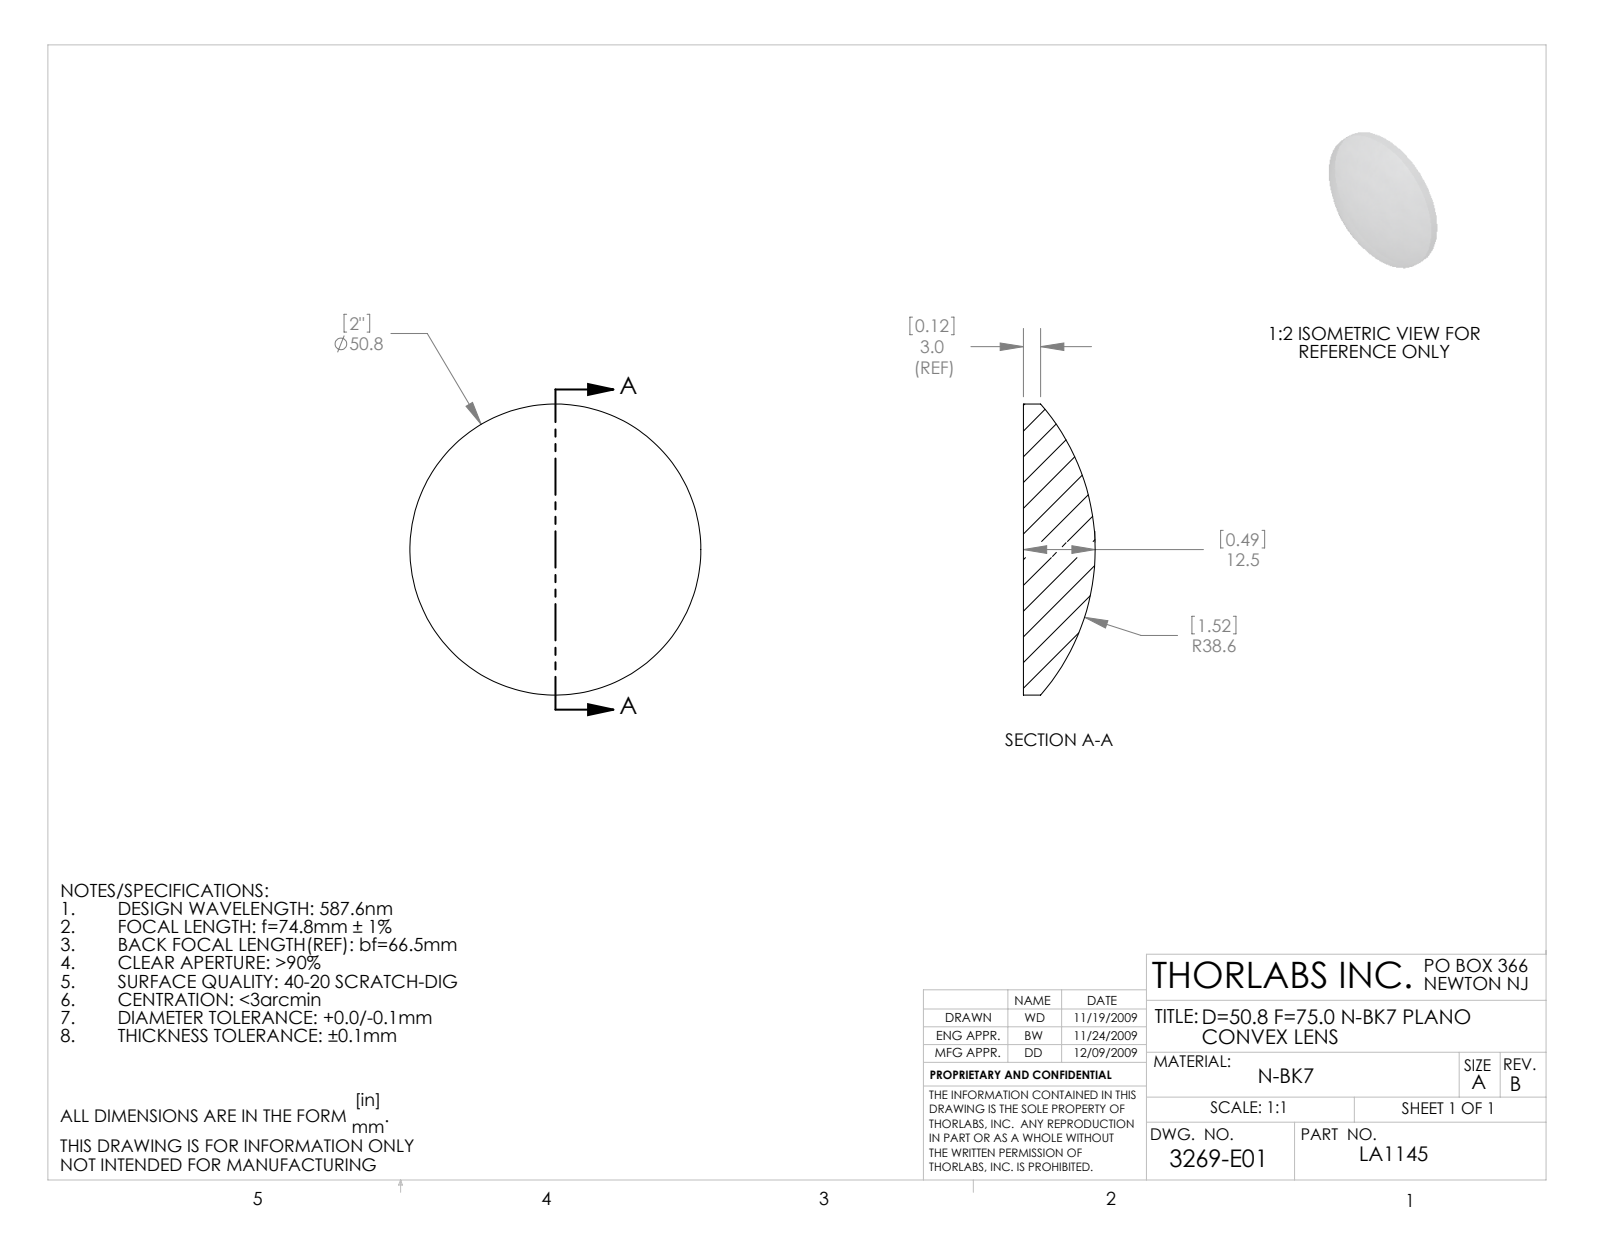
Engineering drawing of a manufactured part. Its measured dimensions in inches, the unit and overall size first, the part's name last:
Units: inches
Overall size (bounding box): 2 × 2 × 0.493
Round bosses / shafts (diameter × count): ⌀2 ×1
Volume: 0.987 in³ · Surface area: 7.466 in²
Bodies: 1 solid, 5 faces (1 planar, 2 cylindrical, 2 other)
Part name (STEP PRODUCT): 3269-E0W
STEP written by: SolidWorks 2009 (AUTOMOTIVE_DESIGN)
